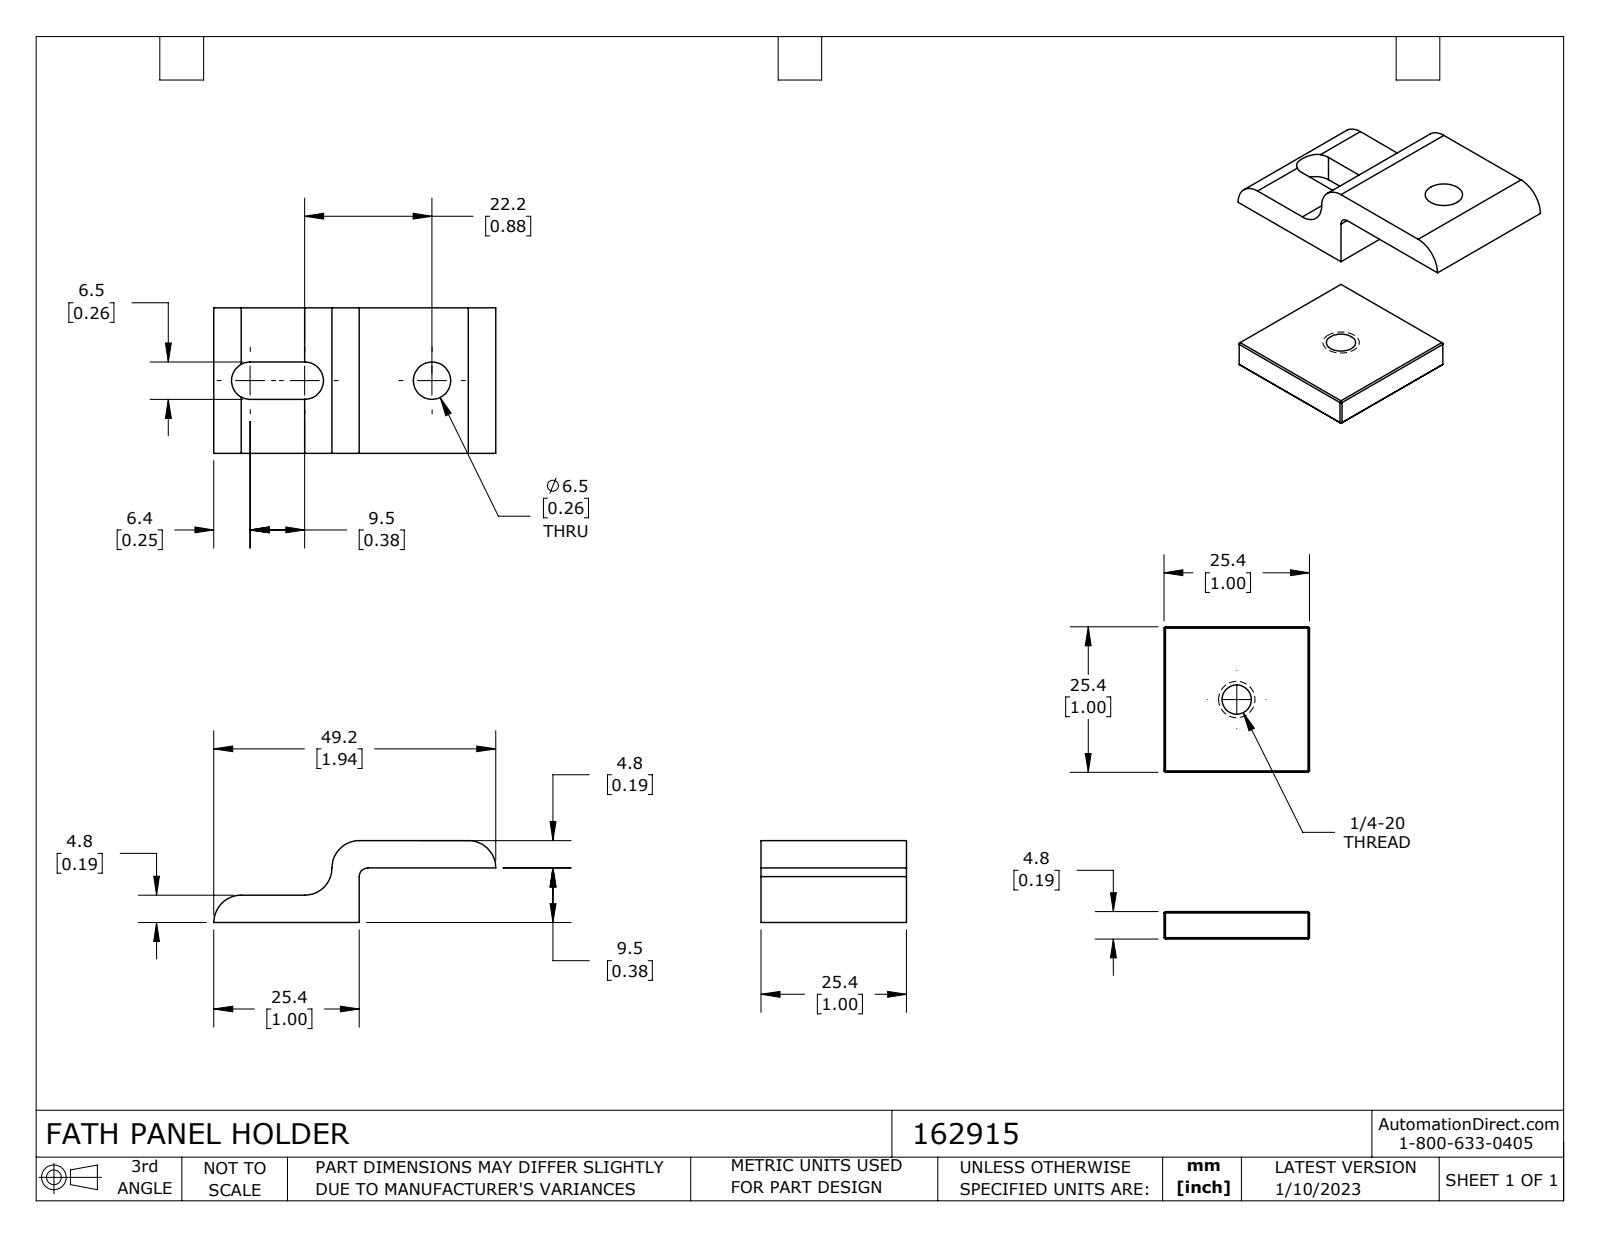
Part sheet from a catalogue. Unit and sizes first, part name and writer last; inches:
Units: inches
Overall size (bounding box): 1.938 × 1.932 × 1
Round holes (diameter × count): ⌀0.201 ×1, ⌀0.257 ×1
Partial cylindrical surfaces — rounded edges, fillets, slot ends (radius × count): R0.129 ×2, R0.188 ×2, R0.188 ×2, R0.059 ×1
Main face-to-face distances: 0.188, 1.744, 1.369, 0.375, 1.181, 1.556, 1, 0.563, 1.933, 0.187
Hole centre spacings: 1
Volume: 0.564 in³ · Surface area: 8.305 in²
Bodies: 2 solids, 49 faces (37 planar, 12 cylindrical, 0 other)
Part name (STEP PRODUCT): 162915
STEP written by: SolidWorks 2021 (CONFIG_CONTROL_DESIGN)
